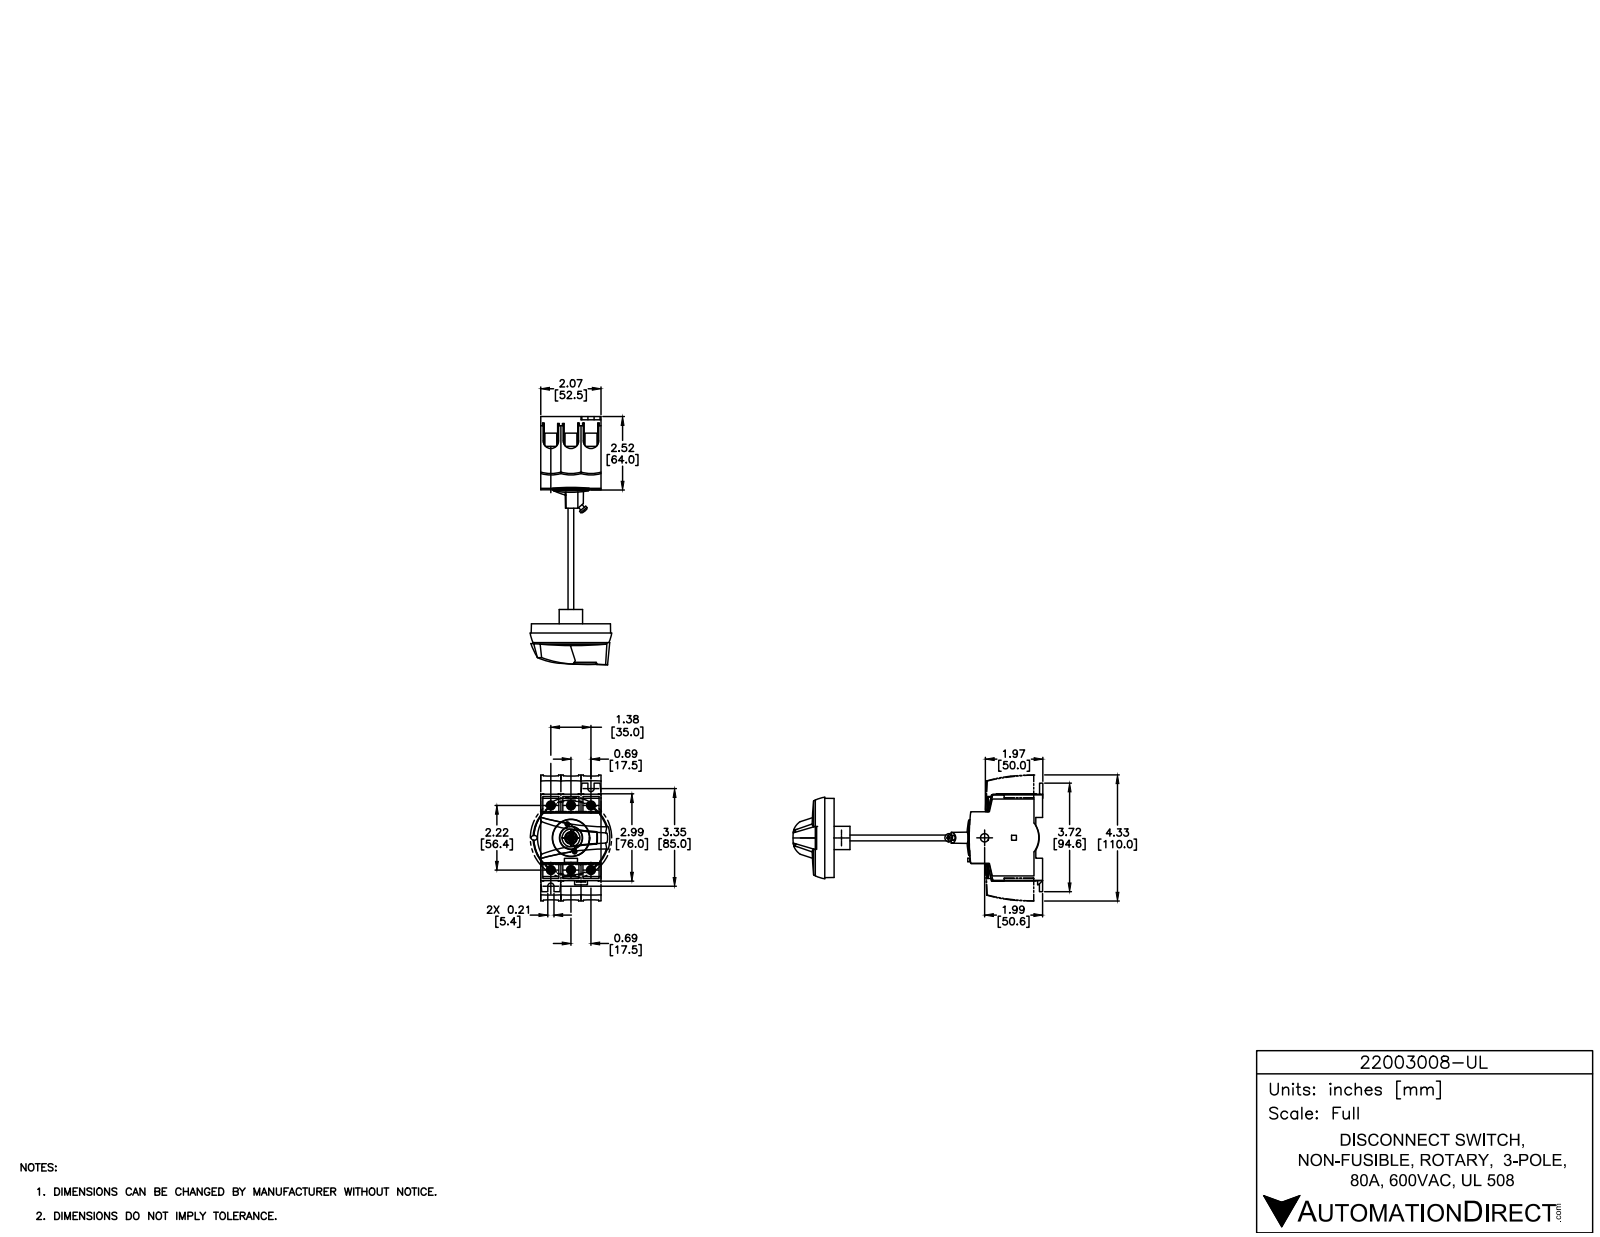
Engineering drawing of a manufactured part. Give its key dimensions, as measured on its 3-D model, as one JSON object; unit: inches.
{"part_name": "22003008-UL", "step_written_by": "SolidWorks 2015 (AUTOMOTIVE_DESIGN)", "units": "inches", "bodies": {"solids": 1, "faces": 238, "planar": 199, "cylindrical": 39, "other": 0}, "overall_size": [3.724, 2.576, 2.067], "volume_in3": 12.81, "surface_area_in2": 42.15, "round_holes": [[0.26, 6], [0.283, 1], [1.26, 1]], "partial_cylinders_radius": [[1.18, 9], [0.012, 4], [0.106, 2], [0.37, 1], [0.827, 1], [7.862, 1]], "face_to_face_distances": [2.067, 2.969, 2.391, 2.382, 0.61, 0.142, 2.827, 0.587, 2.358, 1.772], "hole_center_spacings": [0.689, 1.307, 2.325, 2.22, 1.11, 1.378, 2.613]}
